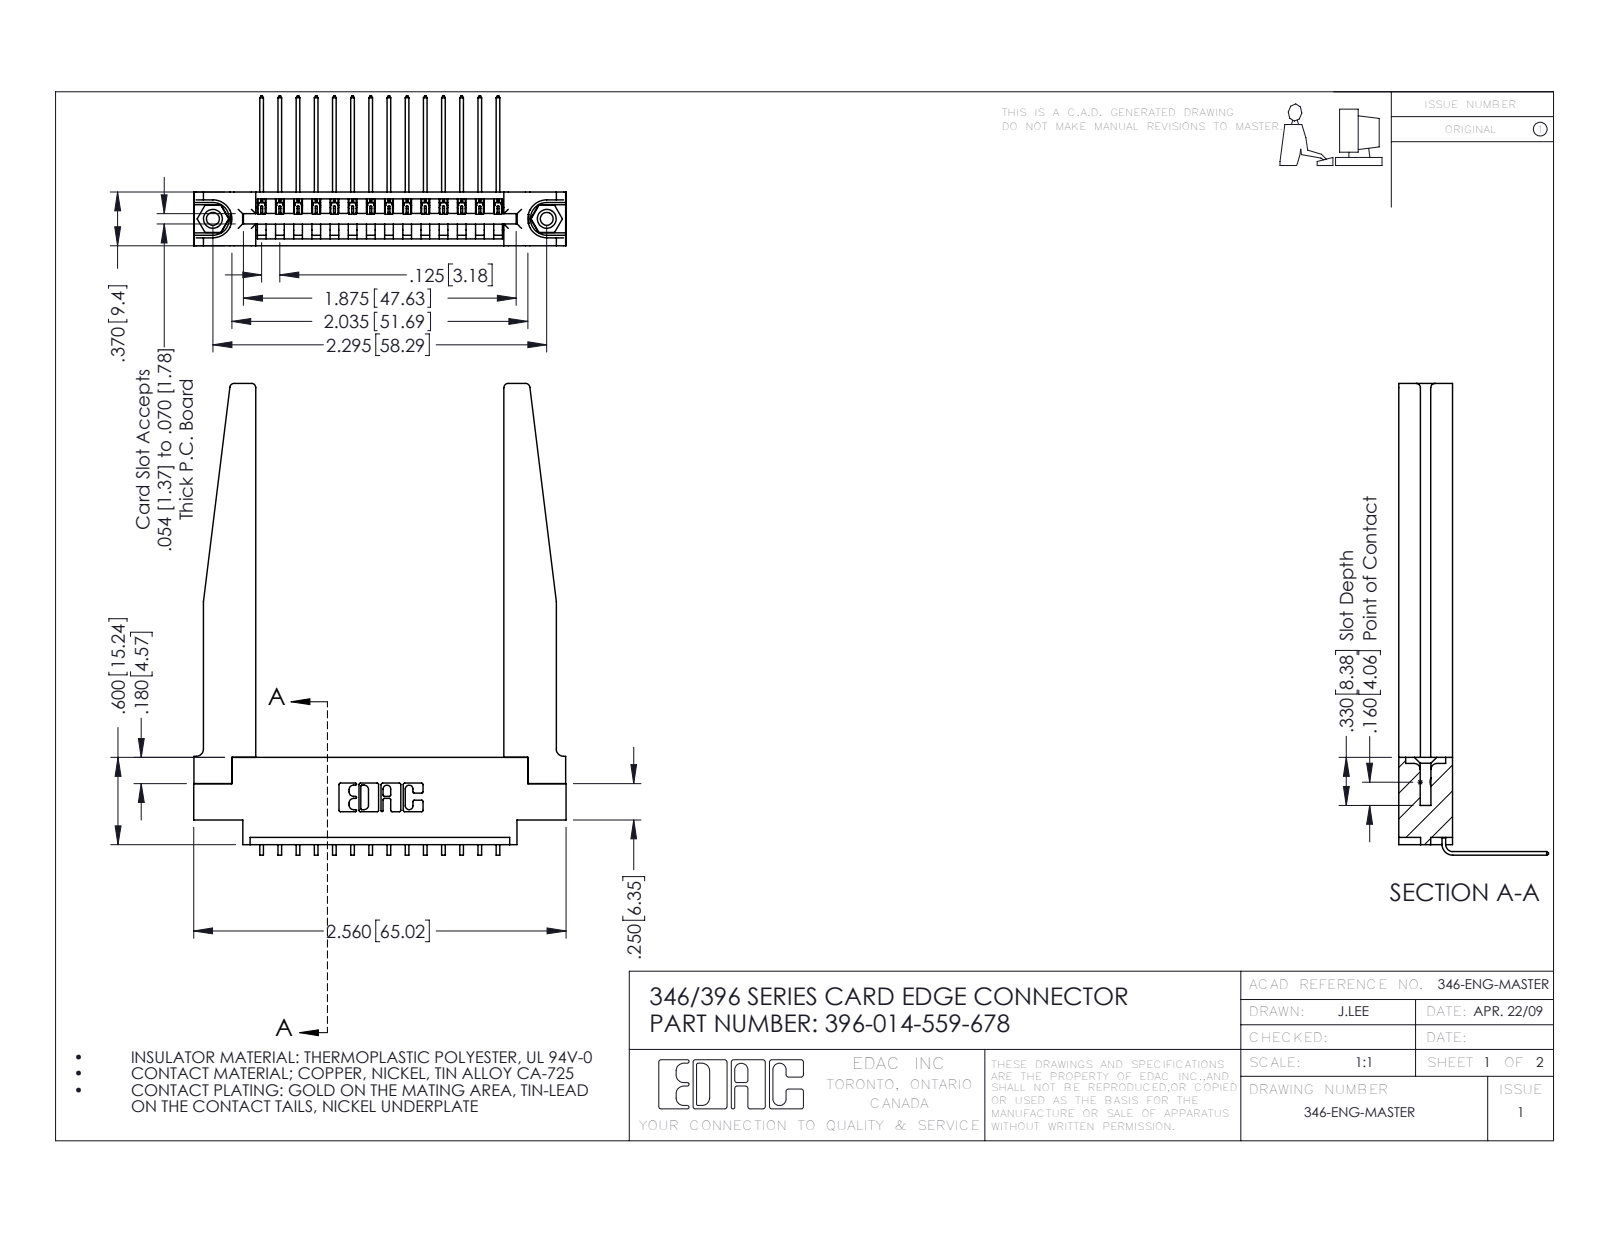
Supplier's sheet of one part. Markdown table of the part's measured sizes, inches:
| quantity | value |
| --- | --- |
| part name | 346 Part_0.170 Offset - 0.156 Dia-TH; 346-220-078_345-220-078; 396-014-559-678; 345-250-001_345-250-001-102 (+1 more) |
| STEP written by | SolidWorks 2016 (CONFIG_CONTROL_DESIGN) |
| units | inches |
| bodies | 19 solids, 1200 faces (810 planar, 338 cylindrical, 52 other) |
| overall size | 3.243 × 2.56 × 1.03 |
| volume | 0.783 in³ |
| surface area | 21.82 in² |
| round holes (diameter × count) | 0.089 × 2, 0.125 × 2, 0.156 × 2, 0.064 × 1 |
| round bosses / shafts (diameter × count) | 0.155 × 2 |
| partial cylindrical surfaces (radius × count) | 0.006 × 28, 0.01 × 22, 0.03 × 8, 0.007 × 6, 0.031 × 6, 0.026 × 3, 0.05 × 3, 0.031 × 2 |
| main face-to-face distances | 0.37, 0.15, 0.072, 0.048, 0.148, 0.322, 0.25, 0.102, 0.22, 0.173 |
| hole center spacings | 0.246, 2.089, 2.295 |
